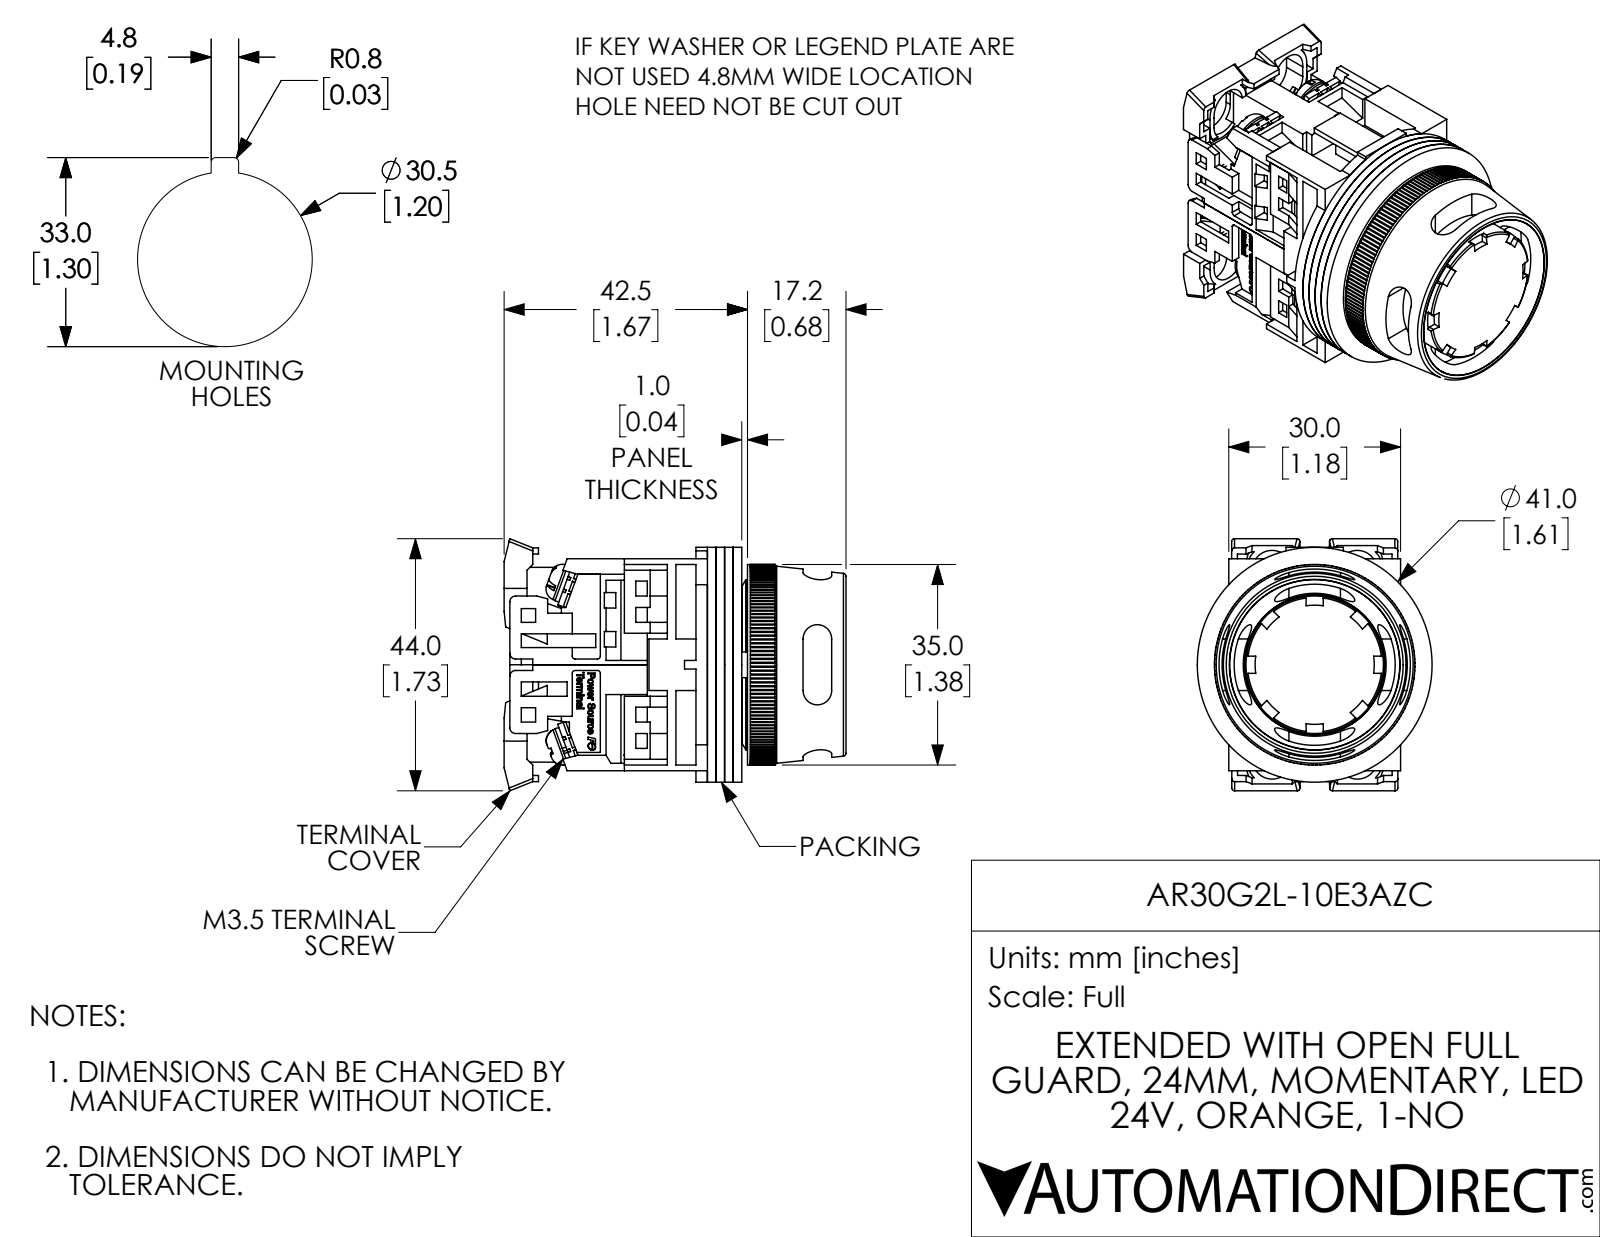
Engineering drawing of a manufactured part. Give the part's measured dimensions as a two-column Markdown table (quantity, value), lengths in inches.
| quantity | value |
| --- | --- |
| part name | AR30G2L-10E3AZC |
| STEP written by | SolidWorks 2017 (AUTOMOTIVE_DESIGN) |
| units | inches |
| bodies | 25 solids, 2179 faces (1508 planar, 458 cylindrical, 213 other) |
| overall size | 2.35 × 1.732 × 1.614 |
| volume | 2.142 in³ |
| surface area | 62.62 in² |
| round holes (diameter × count) | 0.138 × 8, 0.142 × 4, 0.118 × 1, 0.472 × 1, 0.709 × 1, 0.728 × 1, 0.787 × 1, 0.945 × 1, 1.252 × 1 |
| round bosses / shafts (diameter × count) | 0.26 × 4, 0.138 × 4, 1.614 × 1, 1.378 × 1, 1.181 × 1, 0.866 × 1, 0.776 × 1, 0.551 × 1 |
| partial cylindrical surfaces (radius × count) | 0.01 × 160, 0.012 × 16, 0.059 × 16, 0.02 × 12, 0.039 × 4, 0.098 × 4, 0.138 × 4, 0.177 × 4 |
| main face-to-face distances | 0.059, 0.118, 0.039, 0.177, 0.276, 1.417, 0.728, 0.811, 0.079, 1.358 |
| hole center spacings | 0.579, 0.61 |
